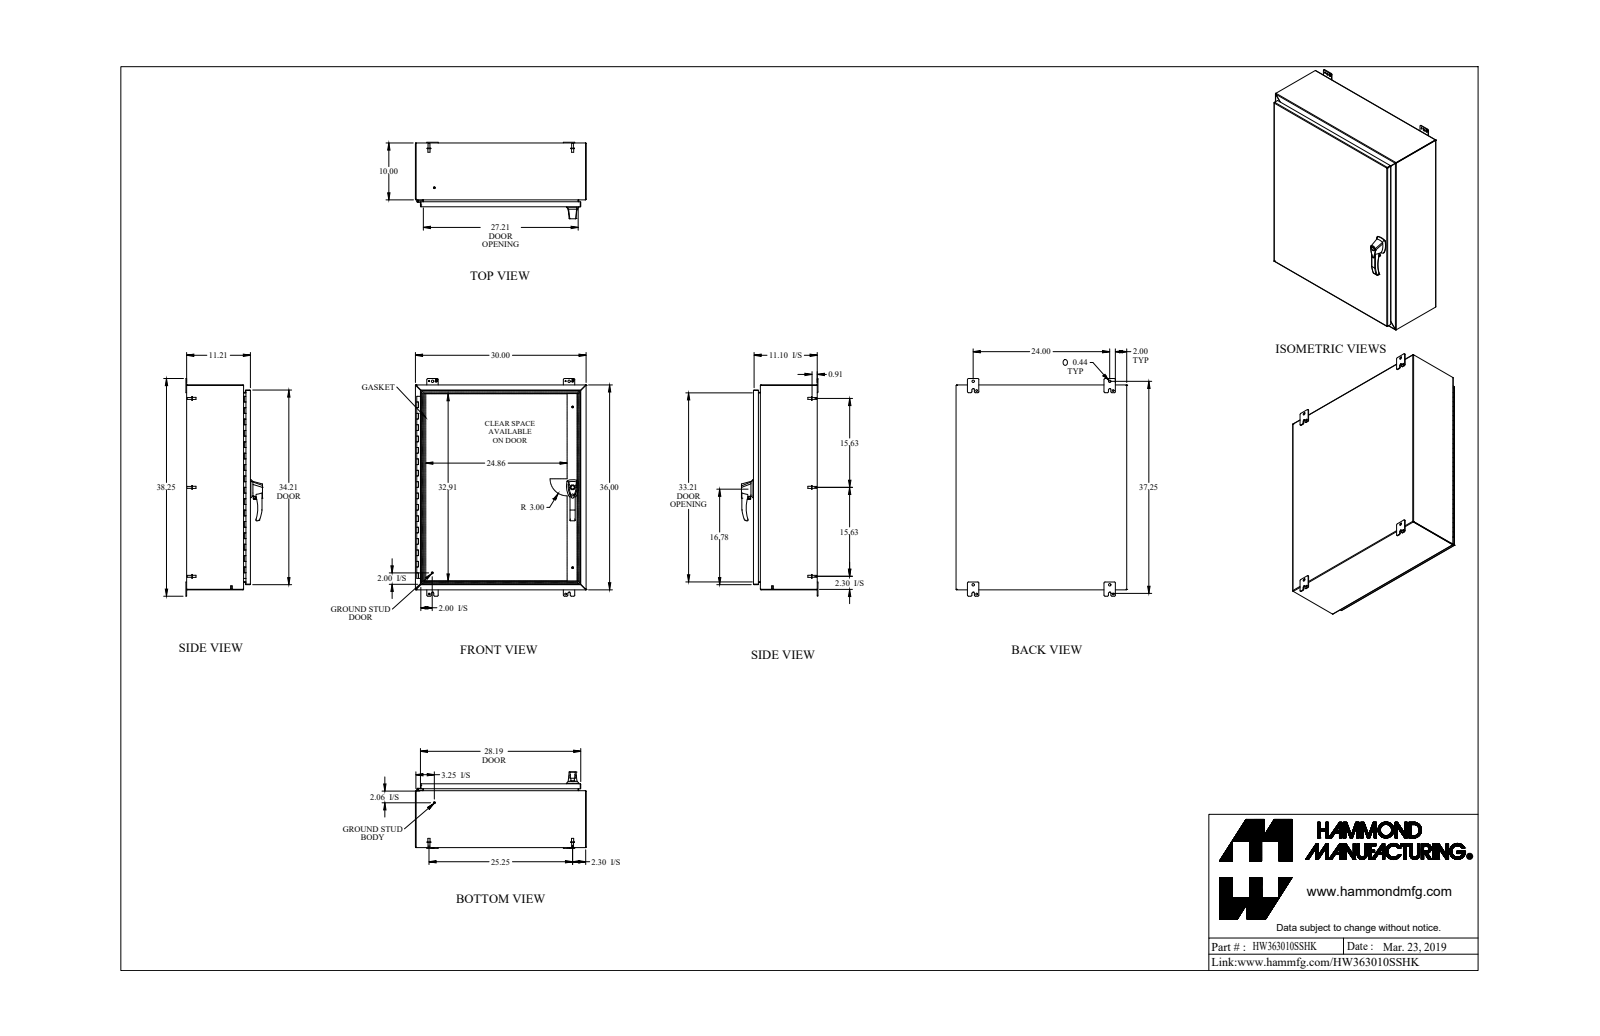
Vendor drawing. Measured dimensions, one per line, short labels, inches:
name: HW363010SSHK
written by: SolidWorks 2018 (AUTOMOTIVE_DESIGN)
unit: in
bodies: 44 solids, 1544 faces (737 planar, 641 cylindrical, 166 other)
size: 38.25 × 30 × 13.45
volume: 312.9 in³; area: 8 258 in²
holes: 6× ⌀0.176, 5× ⌀0.313, 3× ⌀0.25, 3× ⌀0.265, 3× ⌀0.413, 2× ⌀0.196, 2× ⌀0.256, 2× ⌀0.394, 2× ⌀0.437, 1× ⌀0.187, 1× ⌀0.233, 1× ⌀0.33
bosses: 11× ⌀0.375, 7× ⌀0.25, 6× ⌀0.65, 6× ⌀0.332, 6× ⌀0.156, 4× ⌀0.313, 3× ⌀1, 3× ⌀0.51
rounds: 27× R0.25, 24× R0.188, 20× R0.036, 20× R0.108, 12× R0.06, 9× R0.125, 8× R0.045, 8× R0.218
face distances: 0.072, 11.138, 11.066, 11.138, 11.21, 0.072, 29.928, 35.928, 29.856, 30
hole spacings: 1.111, 14.118, 14.119, 28.237, 1.338, 12.78, 14.119, 15.457
